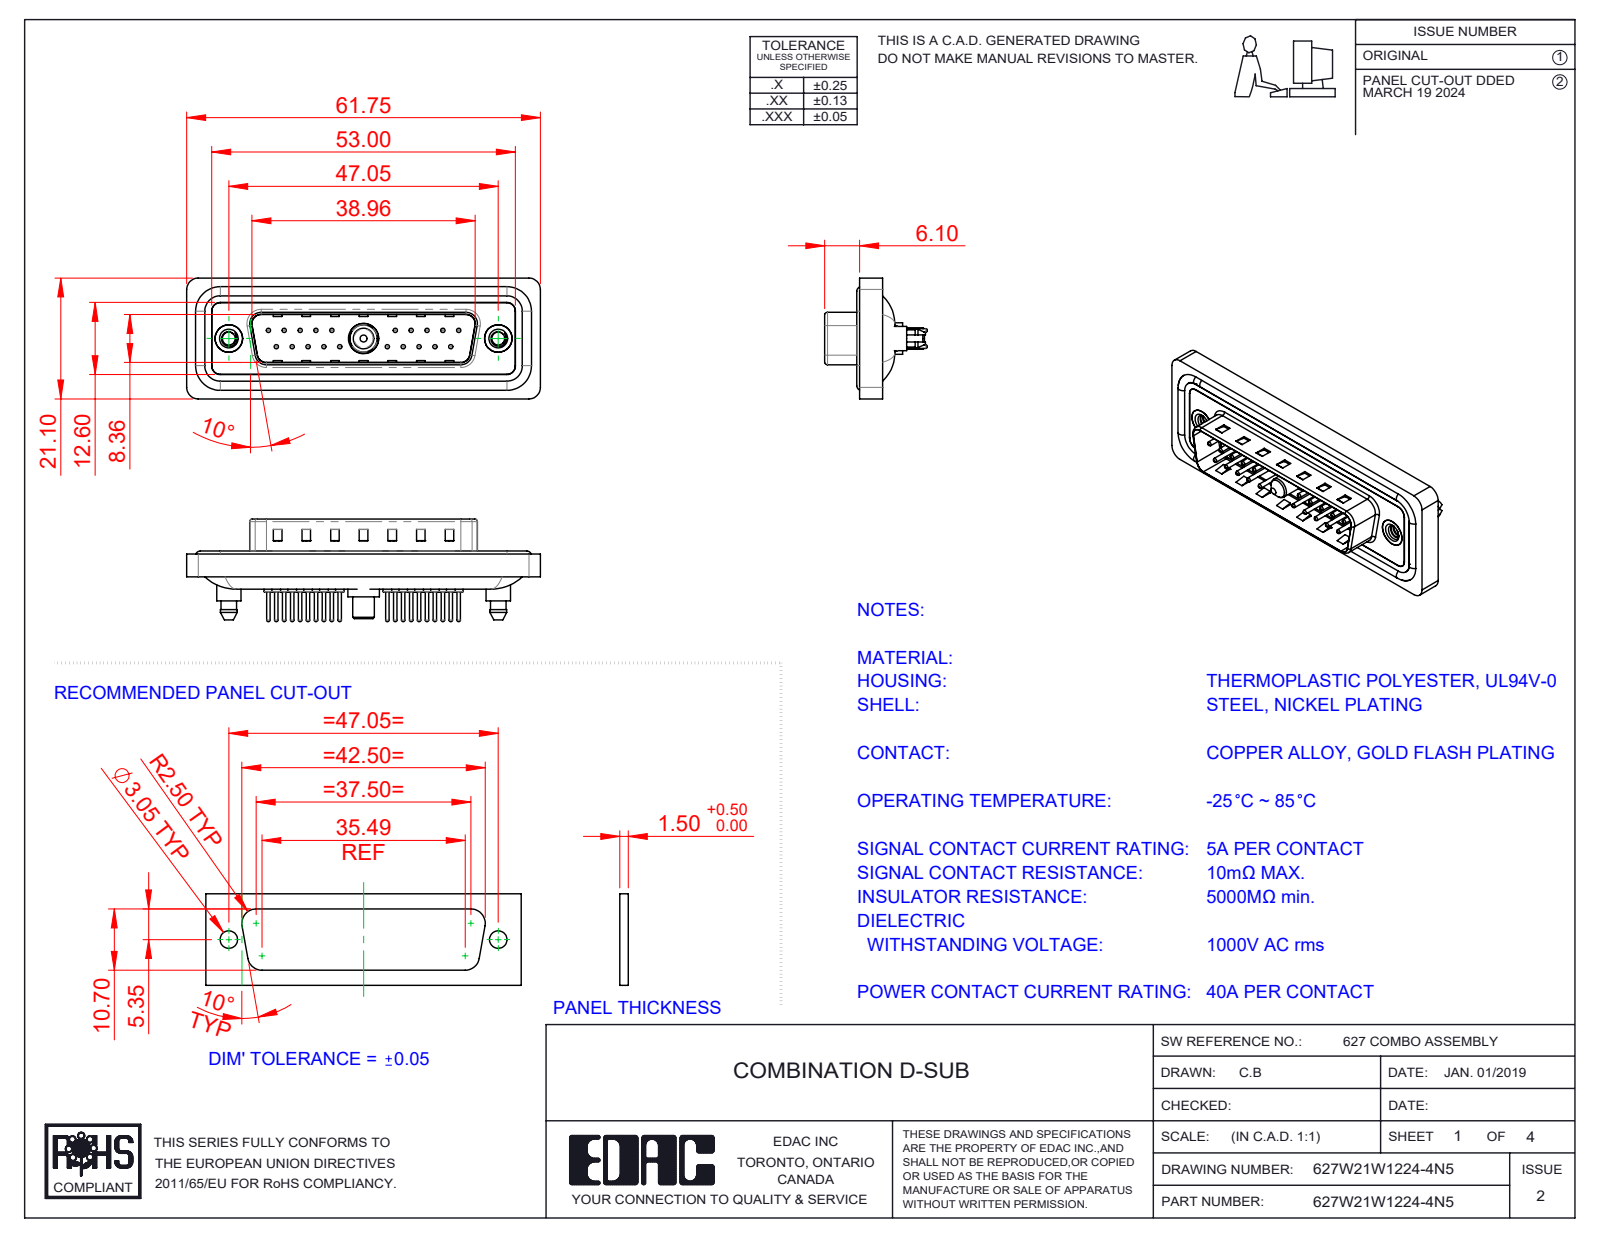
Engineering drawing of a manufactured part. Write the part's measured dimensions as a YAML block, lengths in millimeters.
part_name: "627Combo Contact Row 1_24; 627Combo Housing_21W1; 627W21W1224-4N5; 627Combo Shell Front_25 Contacts (+5 more)"
step_written_by: "SolidWorks 2023 (CONFIG_CONTROL_DESIGN)"
units: millimeters
bodies: {solids: 29, faces: 1312, planar: 375, cylindrical: 519, other: 418}
overall_size: [61.75, 21.1, 17.9]
volume: 7350
surface_area: 12297
round_holes:
  - {diameter: 0.75, count: 20}
  - {diameter: 1.6, count: 20}
  - {diameter: 2, count: 20}
  - {diameter: 2.26, count: 2}
  - {diameter: 4, count: 2}
  - {diameter: 4.8, count: 2}
  - {diameter: 5, count: 2}
  - {diameter: 4.85, count: 1}
  - {diameter: 5.3, count: 1}
round_bosses_or_shafts:
  - {diameter: 1.5, count: 20}
  - {diameter: 0.6, count: 20}
  - {diameter: 1.6, count: 4}
  - {diameter: 5.4, count: 2}
  - {diameter: 4.9, count: 2}
  - {diameter: 4.25, count: 2}
  - {diameter: 5.5, count: 1}
  - {diameter: 5.2, count: 1}
partial_cylinders:
  - {radius: 1.5, count: 24}
  - {radius: 2, count: 18}
  - {radius: 1.6, count: 10}
  - {radius: 0.5, count: 8}
  - {radius: 0.25, count: 4}
  - {radius: 0.6, count: 4}
  - {radius: 0.65, count: 4}
  - {radius: 0.9, count: 4}
face_to_face_distances: [0.4, 1.5, 1.1, 1.6, 3.1, 0.5, 2.9, 4.1, 0.82, 9.58]
hole_center_spacings: [3.16, 2.77, 5.54, 8.31, 5.04, 19.39, 20.97, 22.16]
